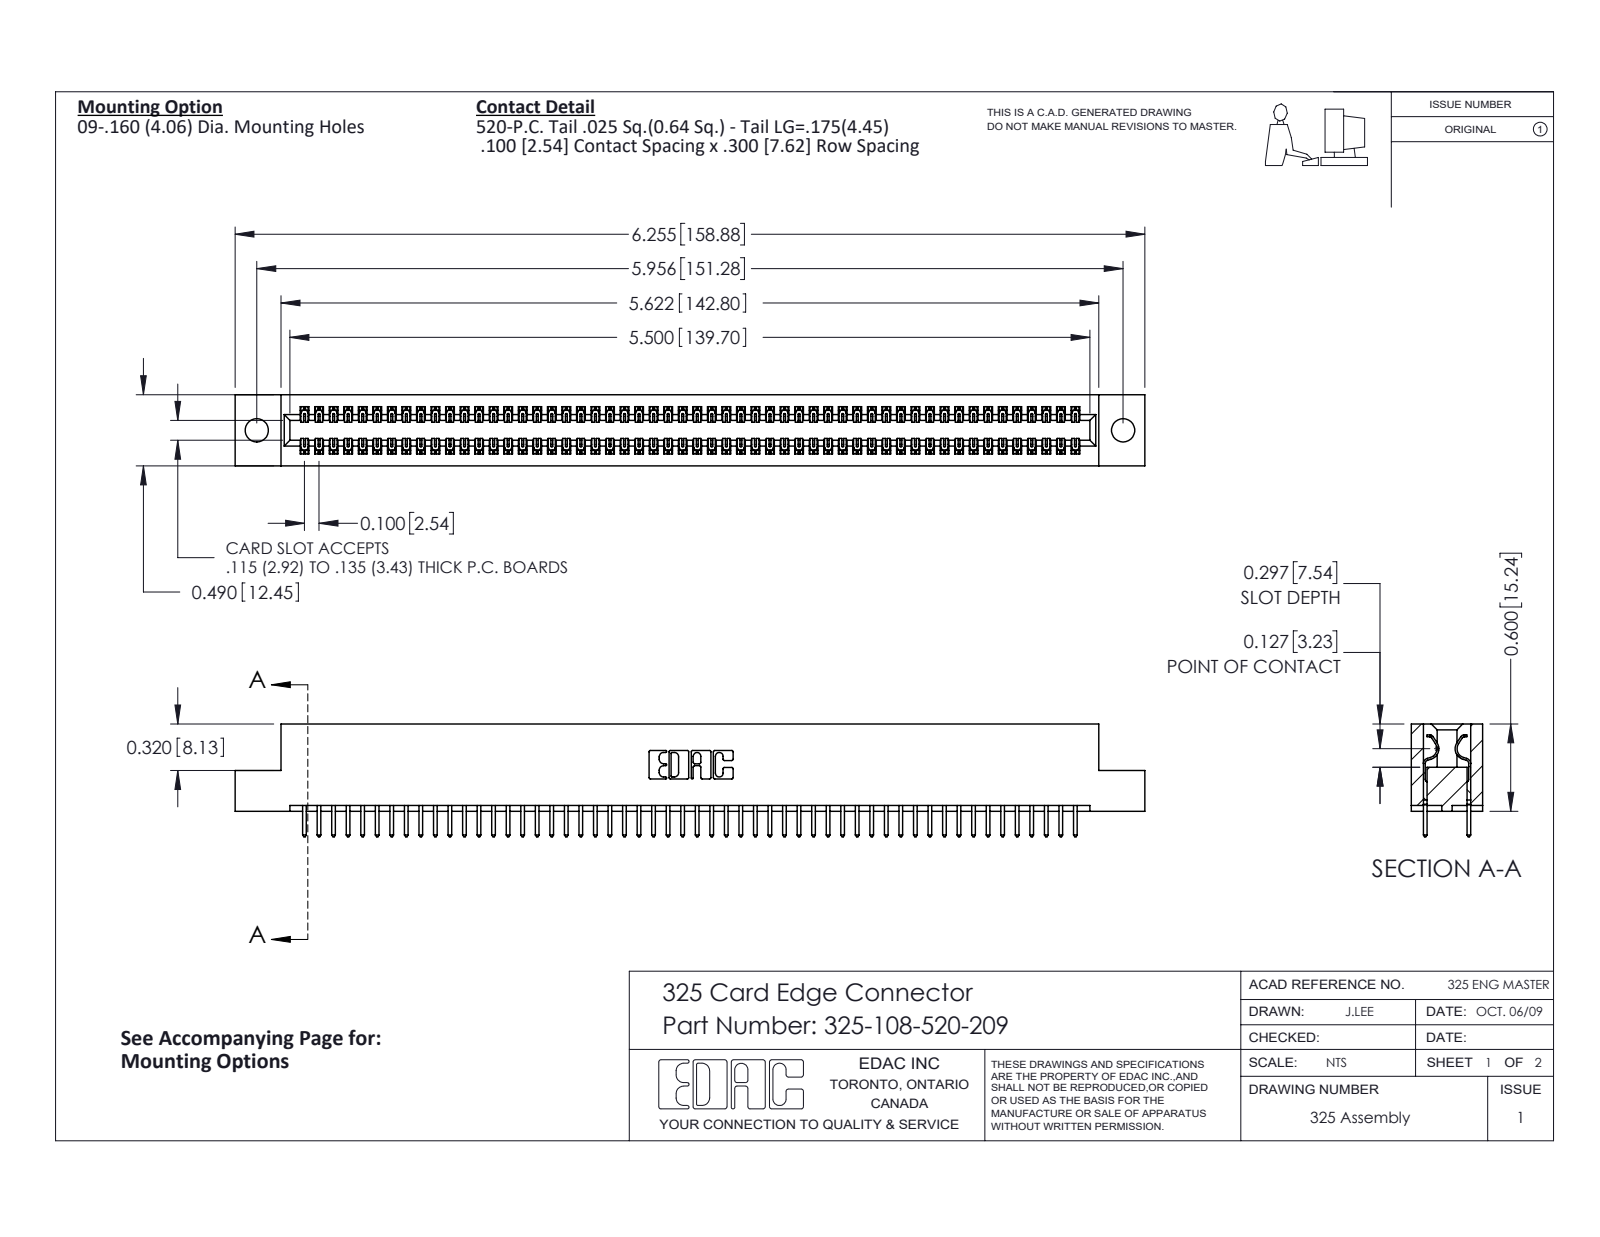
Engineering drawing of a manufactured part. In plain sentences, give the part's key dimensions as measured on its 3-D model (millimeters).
The part is named "325-108-520-209; 325-292-001_325-293-120; 325 Part_.160 TH". Its 3-D file was written by "SolidWorks 2016 (CONFIG_CONTROL_DESIGN)". It is 109 solids with 5730 faces: 3958 planar, 1772 cylindrical and 0 other. Overall it measures 158.9 by 19.7 by 12.4 millimeters. Its volume is 20 370 cubic millimeters and its surface area 24 650 square millimeters. Round holes: 2 of diameter 4.1. Partial cylindrical surfaces (rounded edges, fillets, slot ends): 162 of radius 0.2, 108 of radius 0.3, 22 of radius 0.3, 6 of radius 0.2, 6 of radius 0.8, 3 of radius 0.7, 2 of radius 0.4, 2 of radius 0.6. The main face-to-face distances are 2.1, 10.3, 7.6, 12.4, 2.7, 9.7, 0.6, 8.3, 7, 14.2. The hole center spacings are 151.3.
